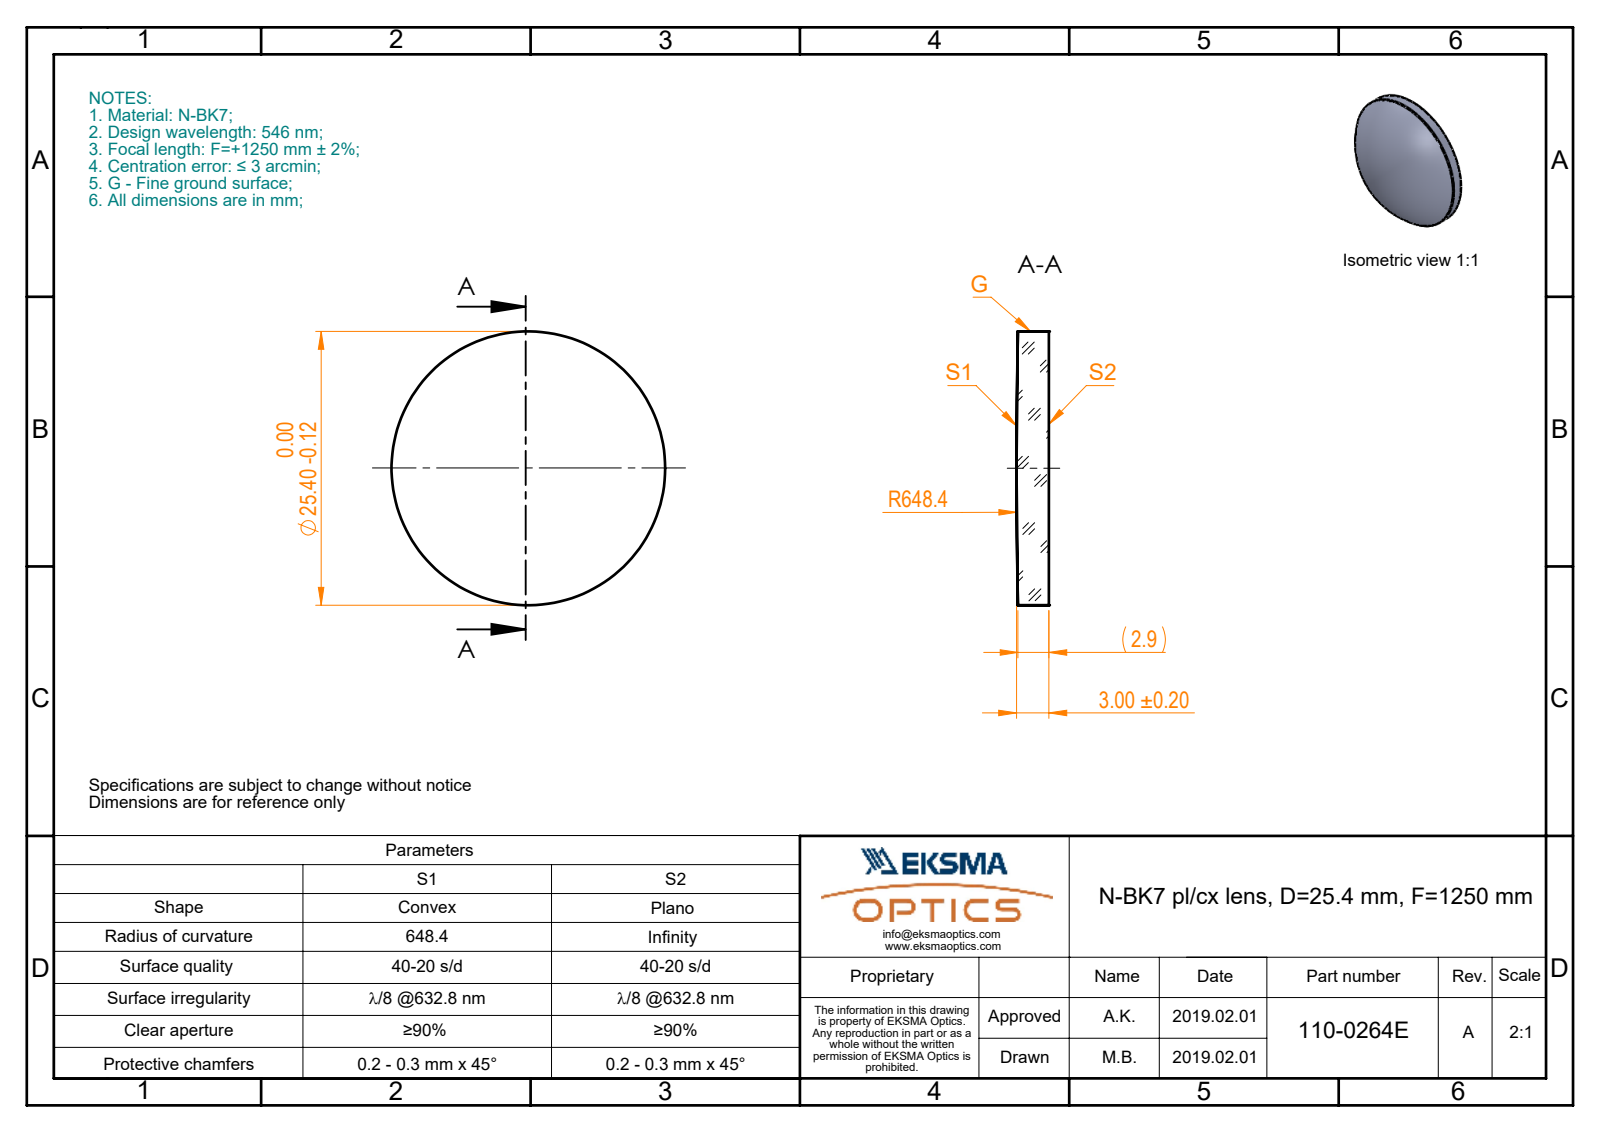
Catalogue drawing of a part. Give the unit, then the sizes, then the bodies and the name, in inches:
Units: inches
Overall size (bounding box): 1 × 1 × 0.118
Round bosses / shafts (diameter × count): ⌀1 ×1
Volume: 0.091 in³ · Surface area: 1.927 in²
Bodies: 1 solid, 5 faces (1 planar, 2 cylindrical, 2 other)
Part name (STEP PRODUCT): 110-0264E BK7 pl-cx 25.4 F1250
STEP written by: SolidWorks 2017 (CONFIG_CONTROL_DESIGN)
